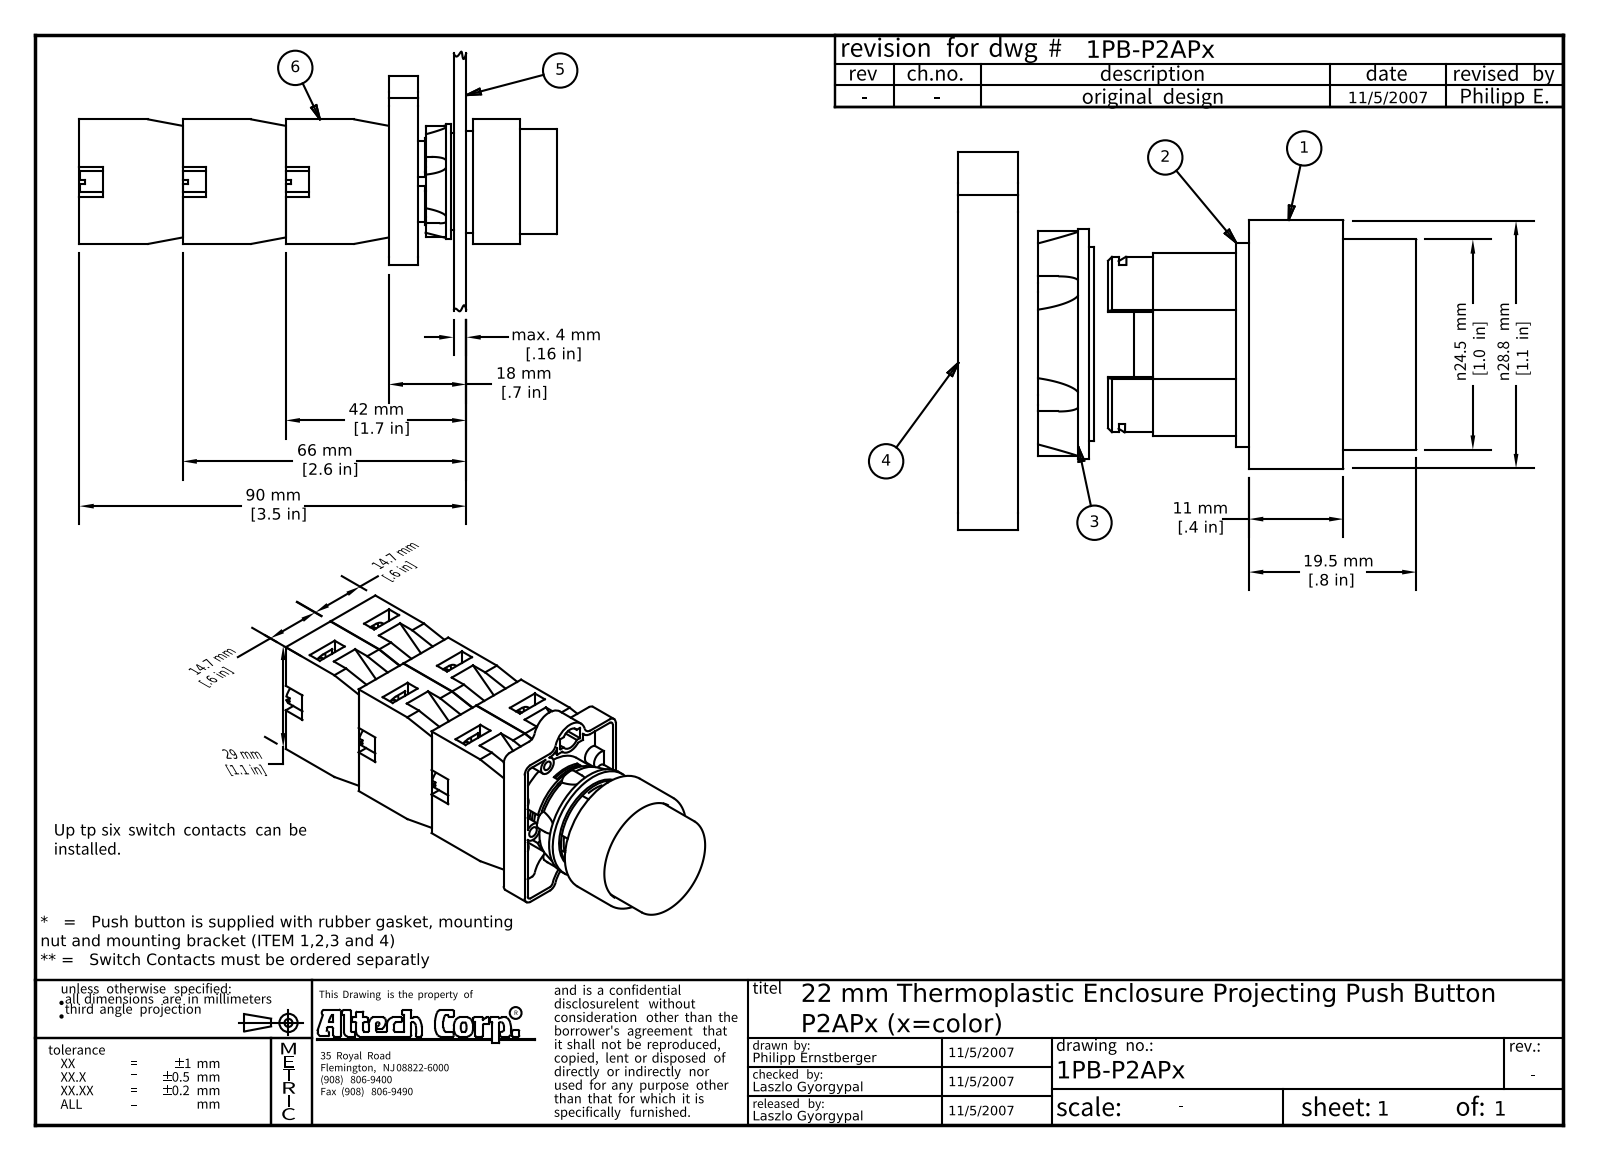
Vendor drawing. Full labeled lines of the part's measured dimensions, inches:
Part name (STEP PRODUCT): P2APx_assembly; P2APx_operator; P2APx; 2PRG1 (+7 more)
STEP written by: Autodesk Inventor 2008 (AUTOMOTIVE_DESIGN)
Units: inches
Bodies: 29 solids, 1168 faces (638 planar, 197 cylindrical, 333 other)
Overall size (bounding box): 4.374 × 2.38 × 1.772
Volume: 4.594 in³ · Surface area: 71.99 in²
Round holes (diameter × count): ⌀0.098 ×6, ⌀0.087 ×2, ⌀0.102 ×2, ⌀0.472 ×1, ⌀0.693 ×1, ⌀0.819 ×1, ⌀0.886 ×1, ⌀0.98 ×1
Round bosses / shafts (diameter × count): ⌀0.118 ×6, ⌀0.108 ×4, ⌀0.059 ×4, ⌀0.197 ×2, ⌀0.165 ×2, ⌀1.142 ×1, ⌀1.055 ×1, ⌀0.965 ×1
Partial cylindrical surfaces — rounded edges, fillets, slot ends (radius × count): R0.039 ×15, R0.059 ×12, R0.079 ×8, R0.089 ×6, R0.118 ×2, R0.13 ×2, R0.197 ×2, R0.102 ×1
Main face-to-face distances: 0.583, 0.579, 0.945, 0.118, 1.89, 1.161, 2.484, 1.539, 1.142, 0.594
Hole centre spacings: 0.257, 1.026, 0.449, 0.512, 0.57, 0.574, 0.676, 0.898
